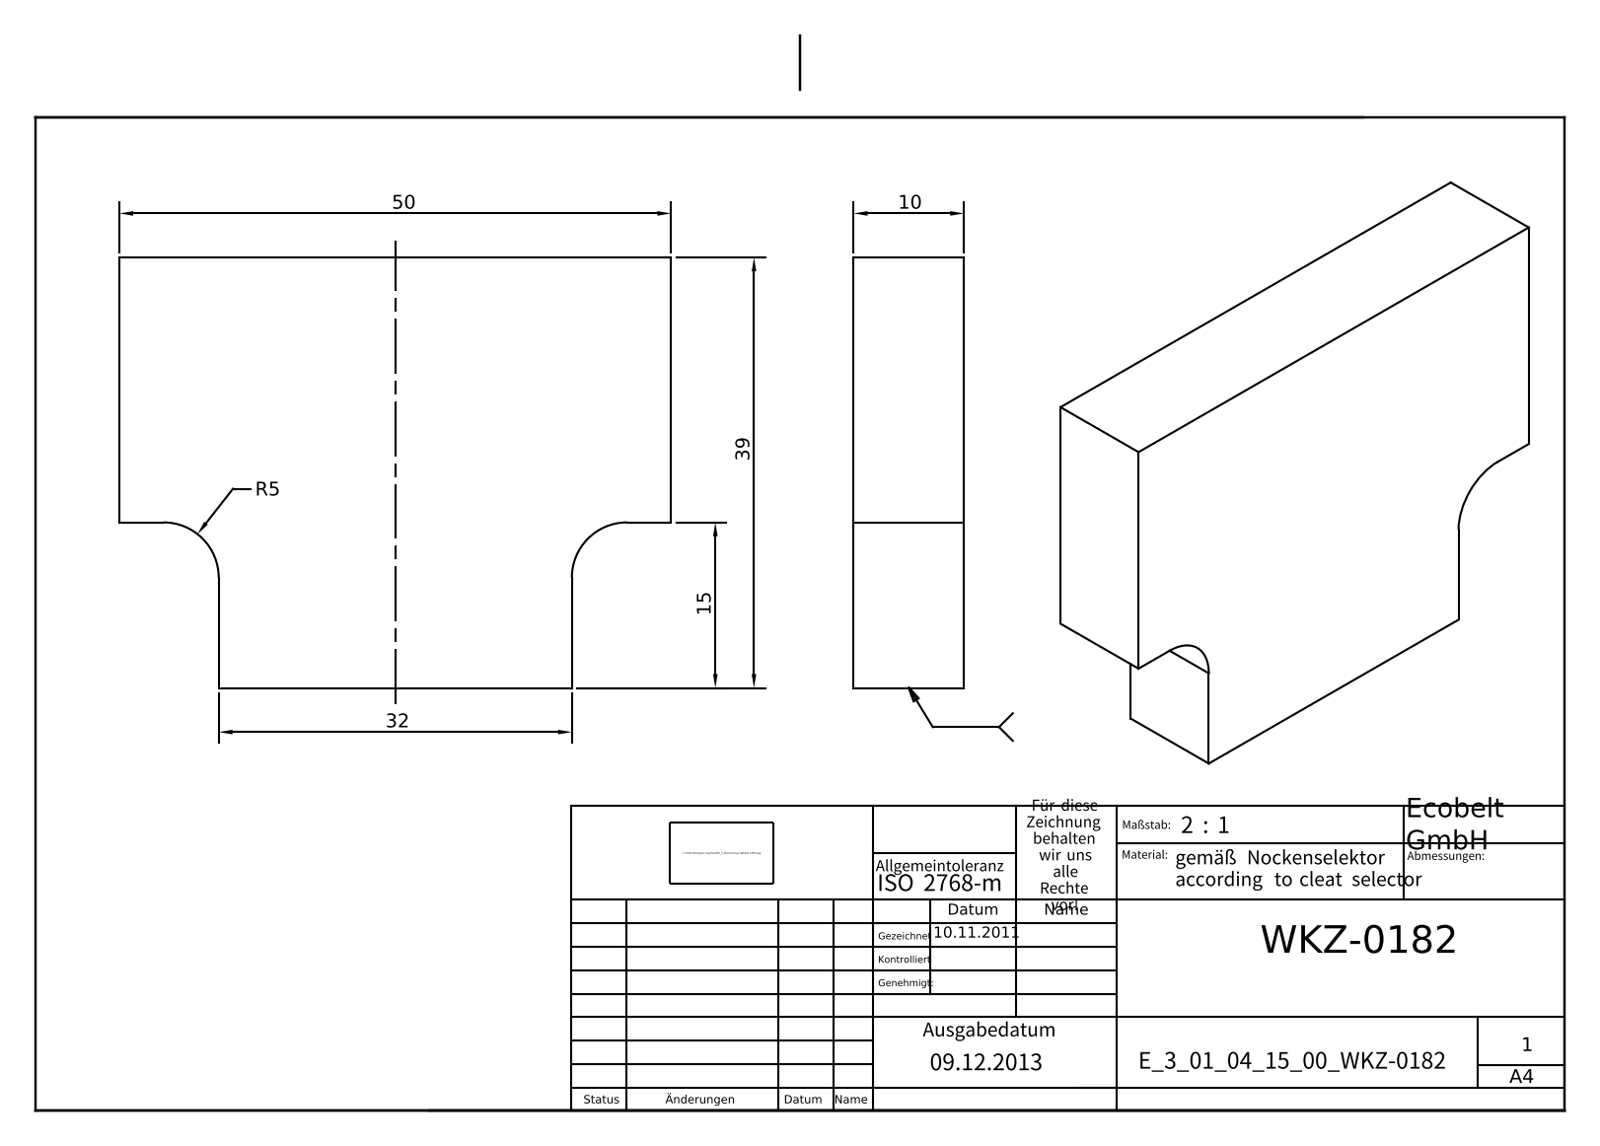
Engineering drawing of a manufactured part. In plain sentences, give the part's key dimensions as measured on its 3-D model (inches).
The part is named "E_3_01_04_15_00_WKZ-0182". Its 3-D file was written by "Autodesk Inventor 2025 (AUTOMOTIVE_DESIGN)". It is 1 solid with 12 faces: 10 planar, 2 cylindrical and 0 other. Overall it measures 1.969 by 1.535 by 0.394 inches. Its volume is 1.032 cubic inches and its surface area 7.934 square inches. Partial cylindrical surfaces (rounded edges, fillets, slot ends): 2 of radius 0.197. The main face-to-face distances are 0.394, 1.535, 1.969, 0.354, 1.614, 1.26, 0.591, 0.945.
